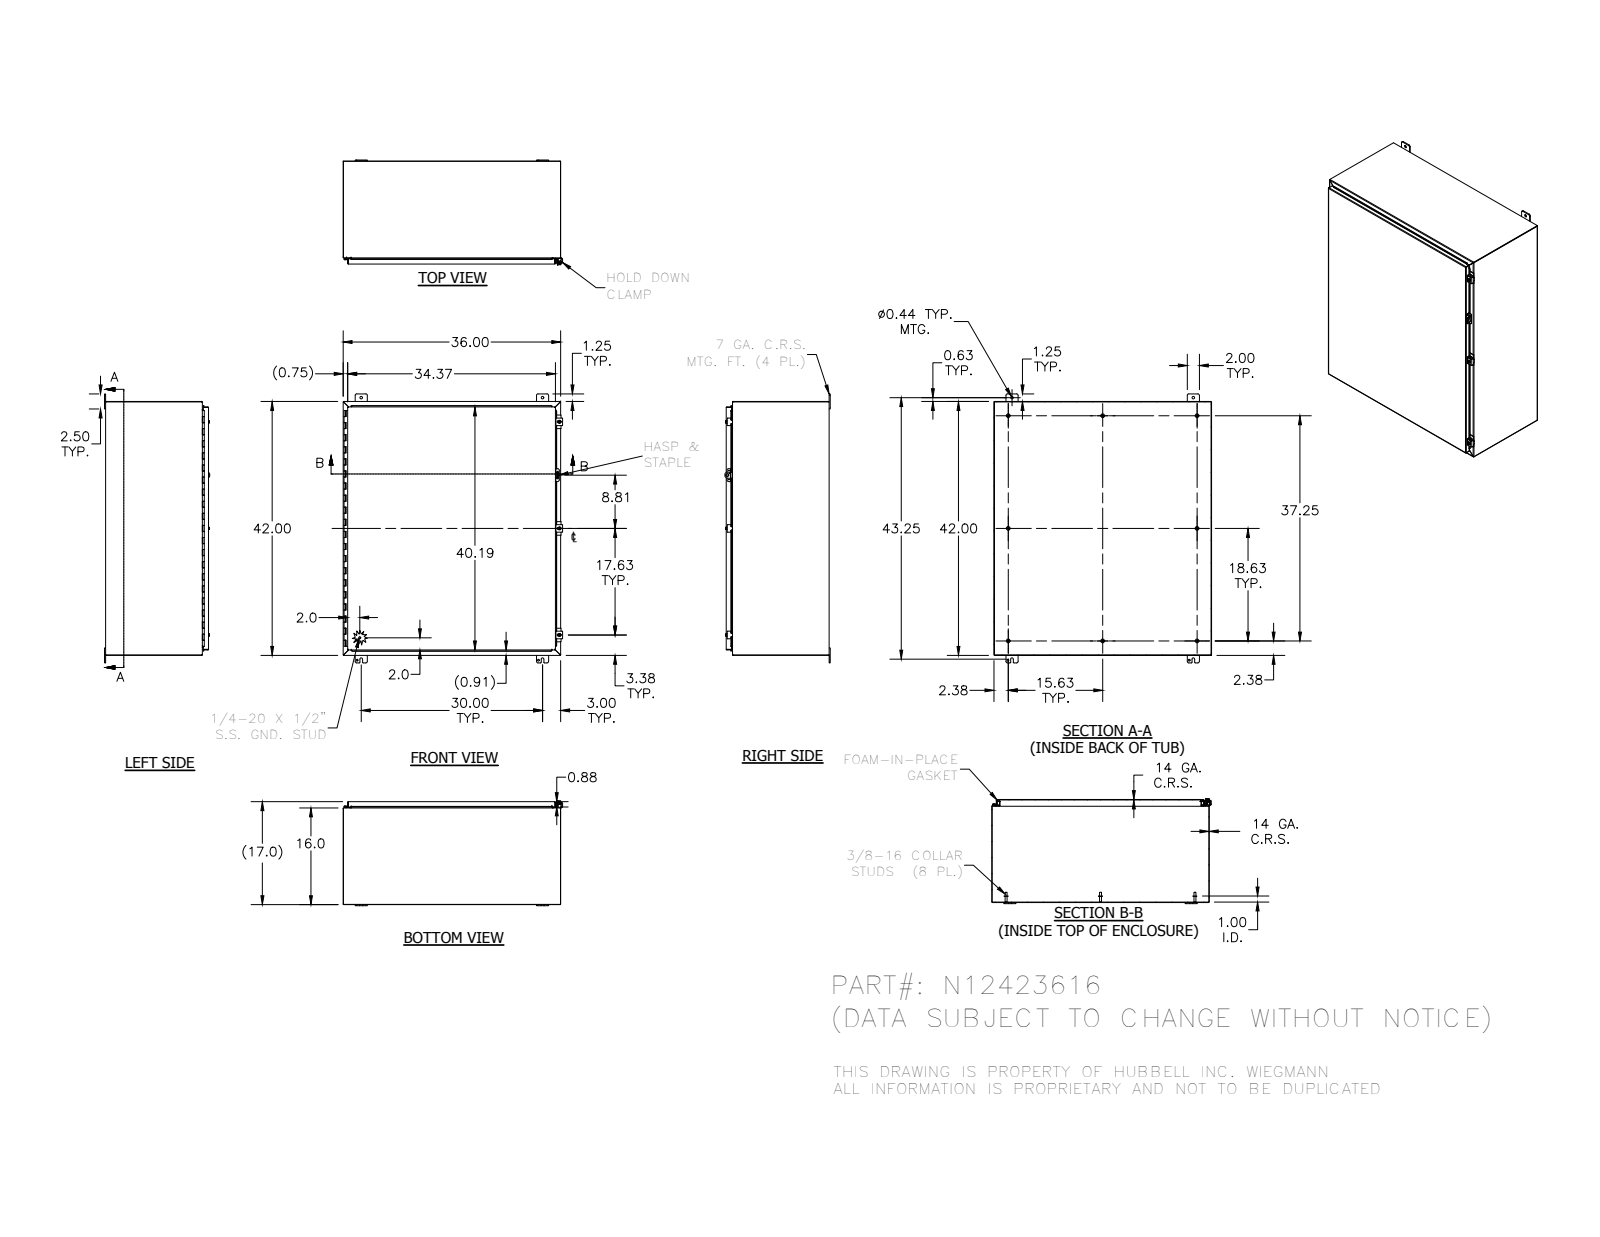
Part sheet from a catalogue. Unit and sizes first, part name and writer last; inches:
Units: inches
Overall size (bounding box): 44.5 × 36.311 × 17.41
Round holes (diameter × count): ⌀0.313 ×4, ⌀0.438 ×4, ⌀0.11 ×3, ⌀0.211 ×3, ⌀0.281 ×3, ⌀0.3 ×3, ⌀0.125 ×1, ⌀0.156 ×1, ⌀0.5 ×1
Round bosses / shafts (diameter × count): ⌀0.625 ×8, ⌀0.33 ×8, ⌀0.25 ×5, ⌀0.52 ×3, ⌀0.5 ×3, ⌀0.35 ×3, ⌀0.115 ×2, ⌀0.337 ×1
Partial cylindrical surfaces — rounded edges, fillets, slot ends (radius × count): R0.03 ×39, R0.125 ×27, R0.25 ×27, R0.031 ×21, R0.105 ×21, R0.063 ×15, R0.1 ×6, R0.141 ×6
Main face-to-face distances: 0.074, 16.959, 16.885, 17.033, 35.926, 41.926, 35.852, 36, 41.852, 42
Hole centre spacings: 1.593, 30, 42, 51.614, 0.791, 8.838, 29.348, 30.72
Volume: 459.6 in³ · Surface area: 12 197 in²
Bodies: 38 solids, 1161 faces (679 planar, 357 cylindrical, 125 other)
Part name (STEP PRODUCT): N12423616; 34840; 38413; N123616TB (+8 more)
STEP written by: Autodesk Inventor 2012 (AUTOMOTIVE_DESIGN)
